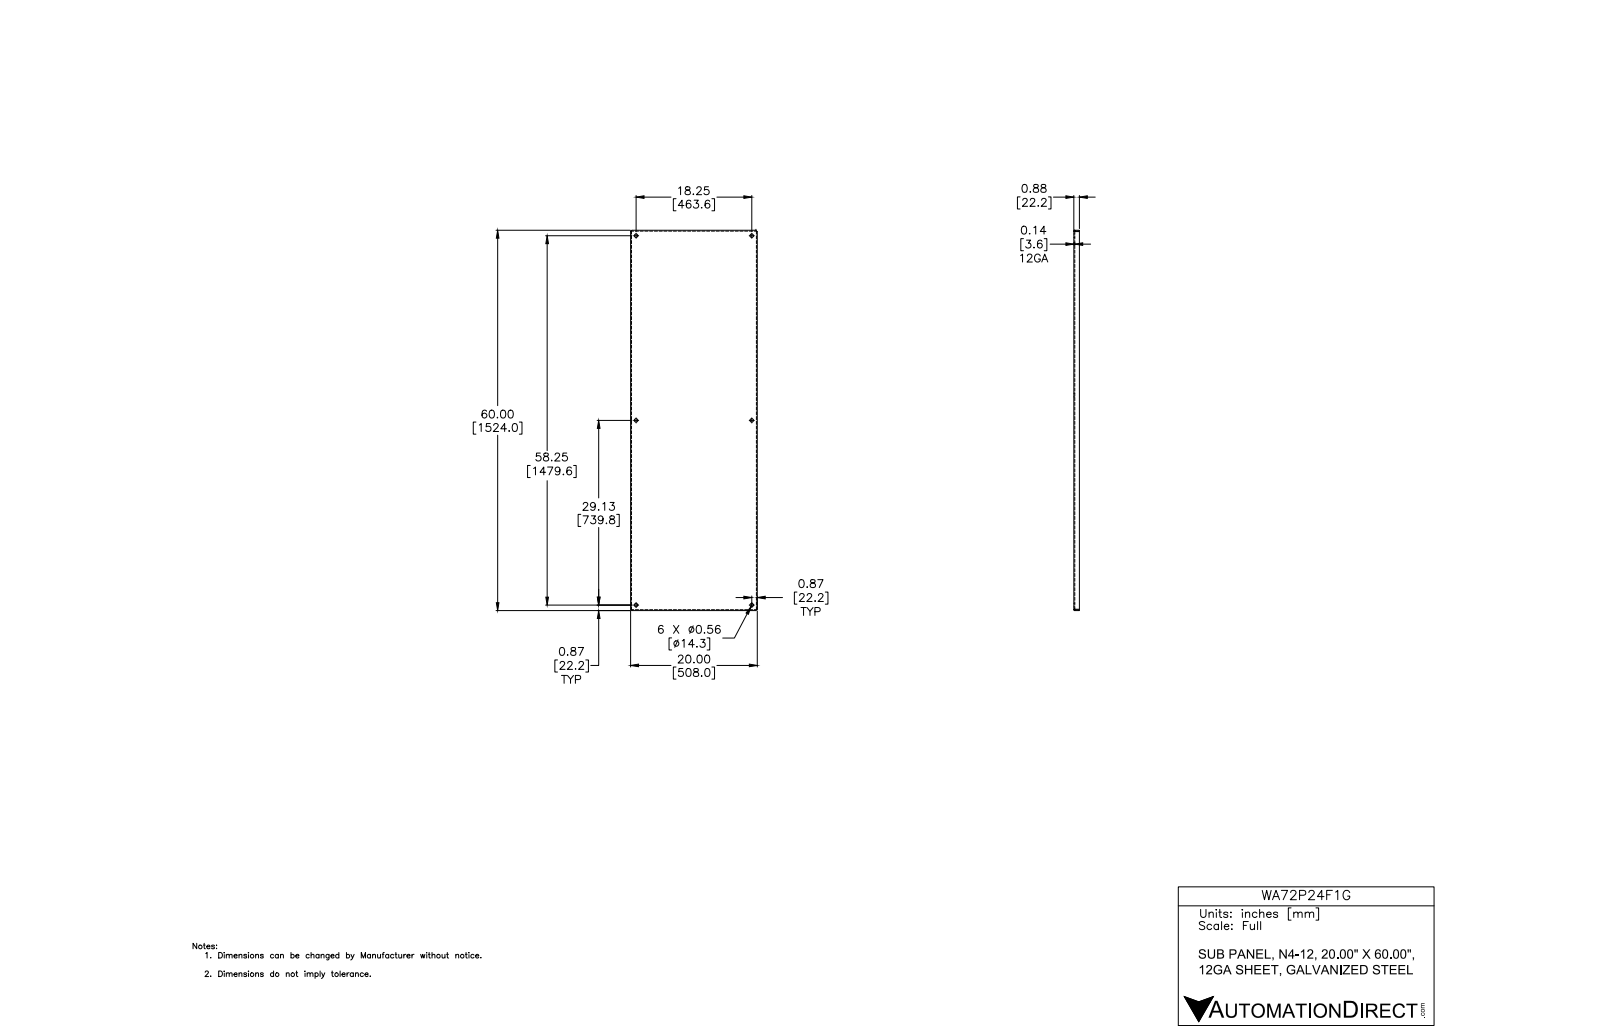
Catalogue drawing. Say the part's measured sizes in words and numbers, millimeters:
The part is named "WA_P_F_G". Its 3-D file was written by "Autodesk Inventor 2012 (AUTOMOTIVE_DESIGN)". It is 1 solid with 44 faces: 22 planar, 14 cylindrical and 8 other. Overall it measures 1524 by 508 by 22.2 millimeters. Its volume is 2 025 000 cubic millimeters and its surface area 1 712 000 square millimeters. Round holes: 6 of diameter 14.3. Partial cylindrical surfaces (rounded edges, fillets, slot ends): 4 of radius 0.4, 4 of radius 2.8. The main face-to-face distances are 2.4, 505.6, 508, 503.3, 1521.6, 1524, 1519.3, 19.8, 22.2, 4.1. The hole center spacings are 873, 463.6, 739.8, 739.8, 1479.6, 1550.5.
